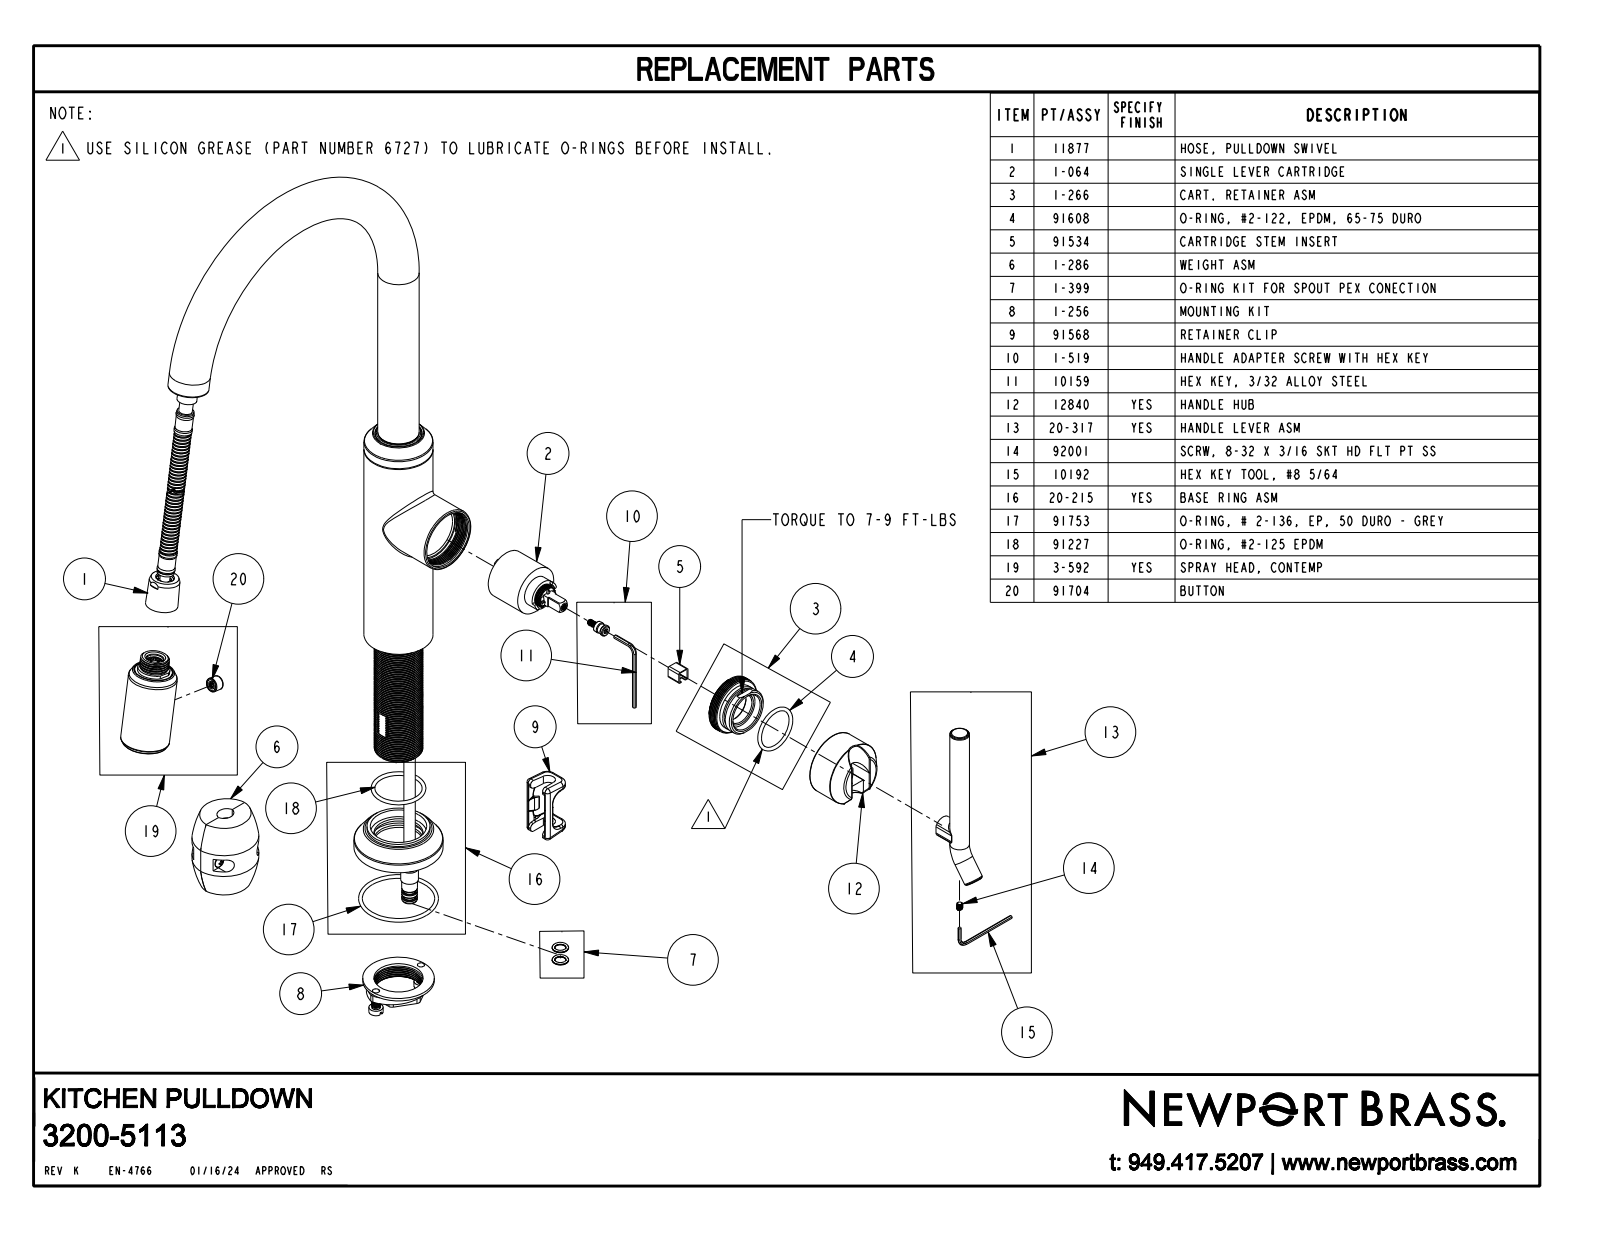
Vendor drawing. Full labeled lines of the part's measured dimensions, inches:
Part name (STEP PRODUCT): 12448
STEP written by: CREO PARAMETRIC BY PTC INC, 2018400 (CONFIG_CONTROL_DESIGN)
Units: inches
Bodies: 1 solid, 323 faces (122 planar, 95 cylindrical, 106 other)
Overall size (bounding box): 17.278 × 11.107 × 5.045
Volume: 49.15 in³ · Surface area: 149.9 in²
Round holes (diameter × count): ⌀0.05 ×20, ⌀0.492 ×1, ⌀0.622 ×1, ⌀0.89 ×1
Round bosses / shafts (diameter × count): ⌀1.14 ×2, ⌀0.54 ×2, ⌀2.451 ×1, ⌀1.9 ×1, ⌀1.8 ×1, ⌀1.61 ×1, ⌀1.35 ×1, ⌀1.124 ×1
Partial cylindrical surfaces — rounded edges, fillets, slot ends (radius × count): R0.337 ×5, R0.02 ×4, R0.12 ×4, R0.06 ×2, R0.297 ×1
Main face-to-face distances: 7.43, 0.04, 0.49, 0.45, 1.144, 1.104, 0.654, 0.675, 0.07, 0.604
Hole centre spacings: 0.341, 0.442, 0.376, 0.118, 0.232, 0.67, 0.608, 0.715
